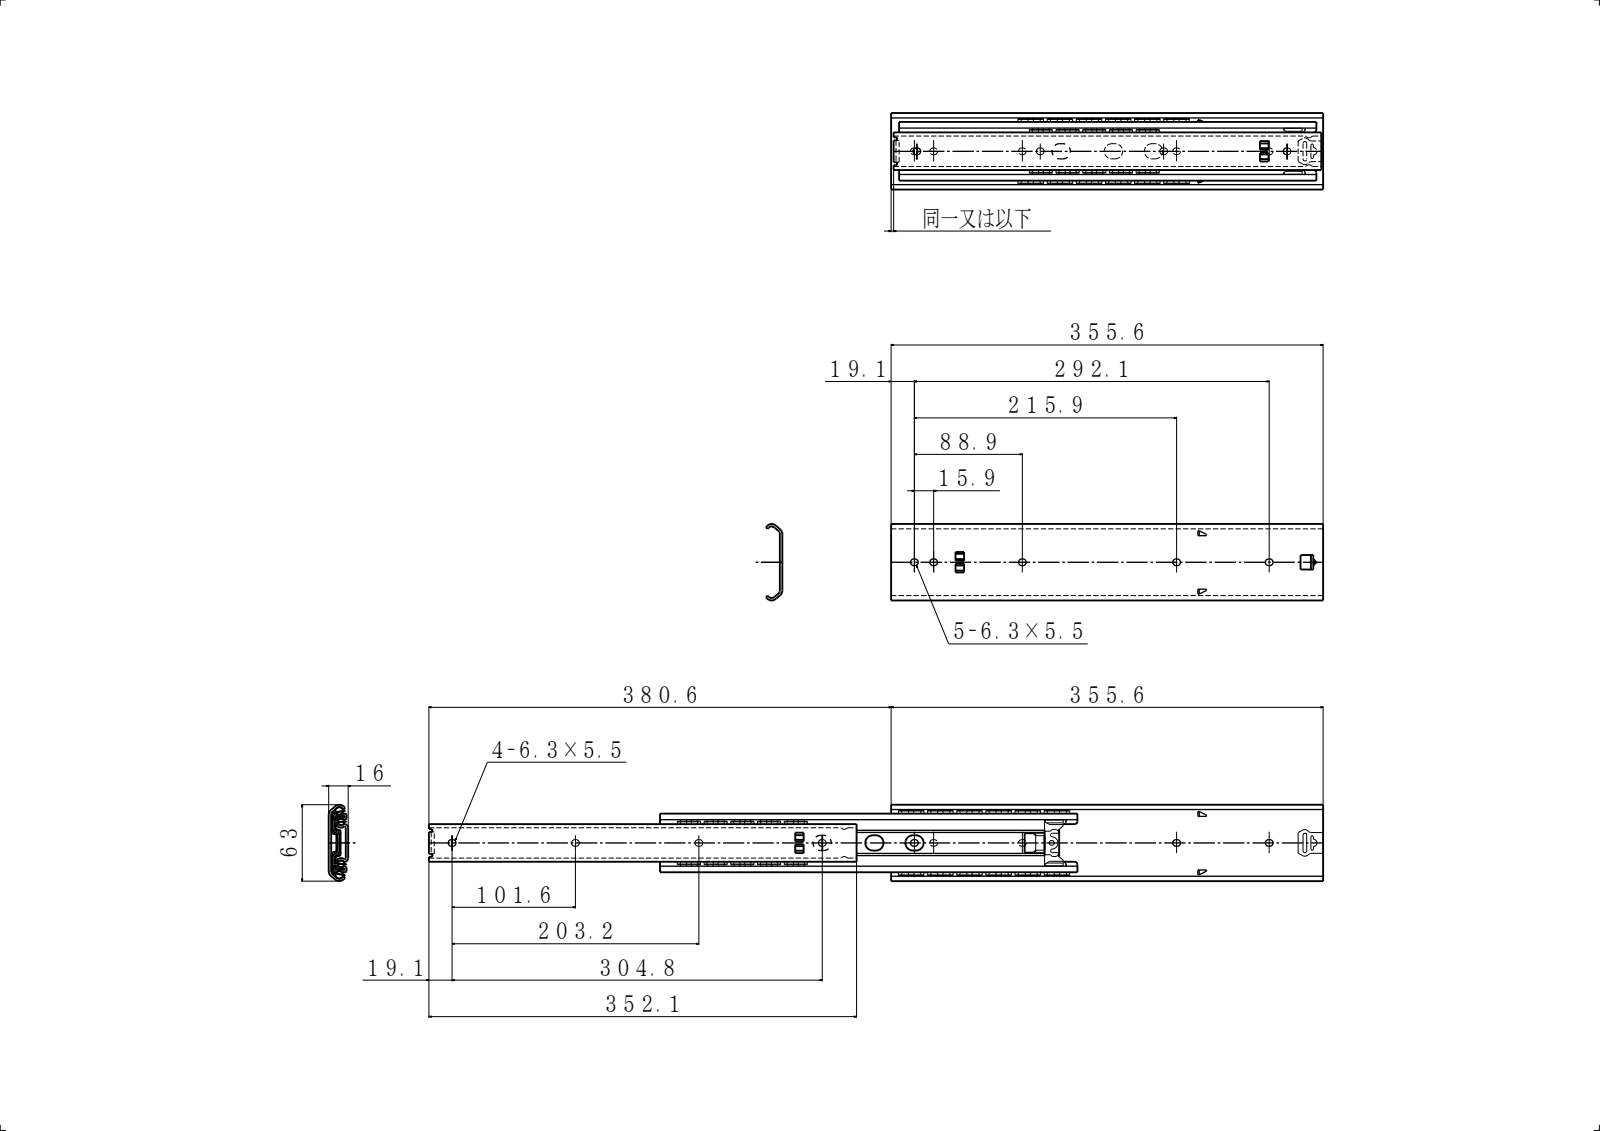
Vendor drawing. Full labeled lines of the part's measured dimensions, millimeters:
Part name (STEP PRODUCT): PN160A; PN68; PN161A; C630-14 IM (+5 more)
STEP written by: SolidWorks 2019 (CONFIG_CONTROL_DESIGN)
Units: millimetres
Bodies: 10 solids, 637 faces (392 planar, 243 cylindrical, 2 other)
Overall size (bounding box): 736.72 × 63 × 16
Volume: 142 752 mm³ · Surface area: 161 989 mm²
Round holes (diameter × count): ⌀5.4 ×1
Round bosses / shafts (diameter × count): ⌀5 ×1
Partial cylindrical surfaces — rounded edges, fillets, slot ends (radius × count): R1 ×22, R0.5 ×20, R2.75 ×18, R2 ×16, R0.3 ×12, R1.2 ×10, R0.2 ×8, R1.6 ×8
Main face-to-face distances: 2, 14, 1.56, 12, 16, 4.08, 1.3, 12.7, 2.86, 11.14
